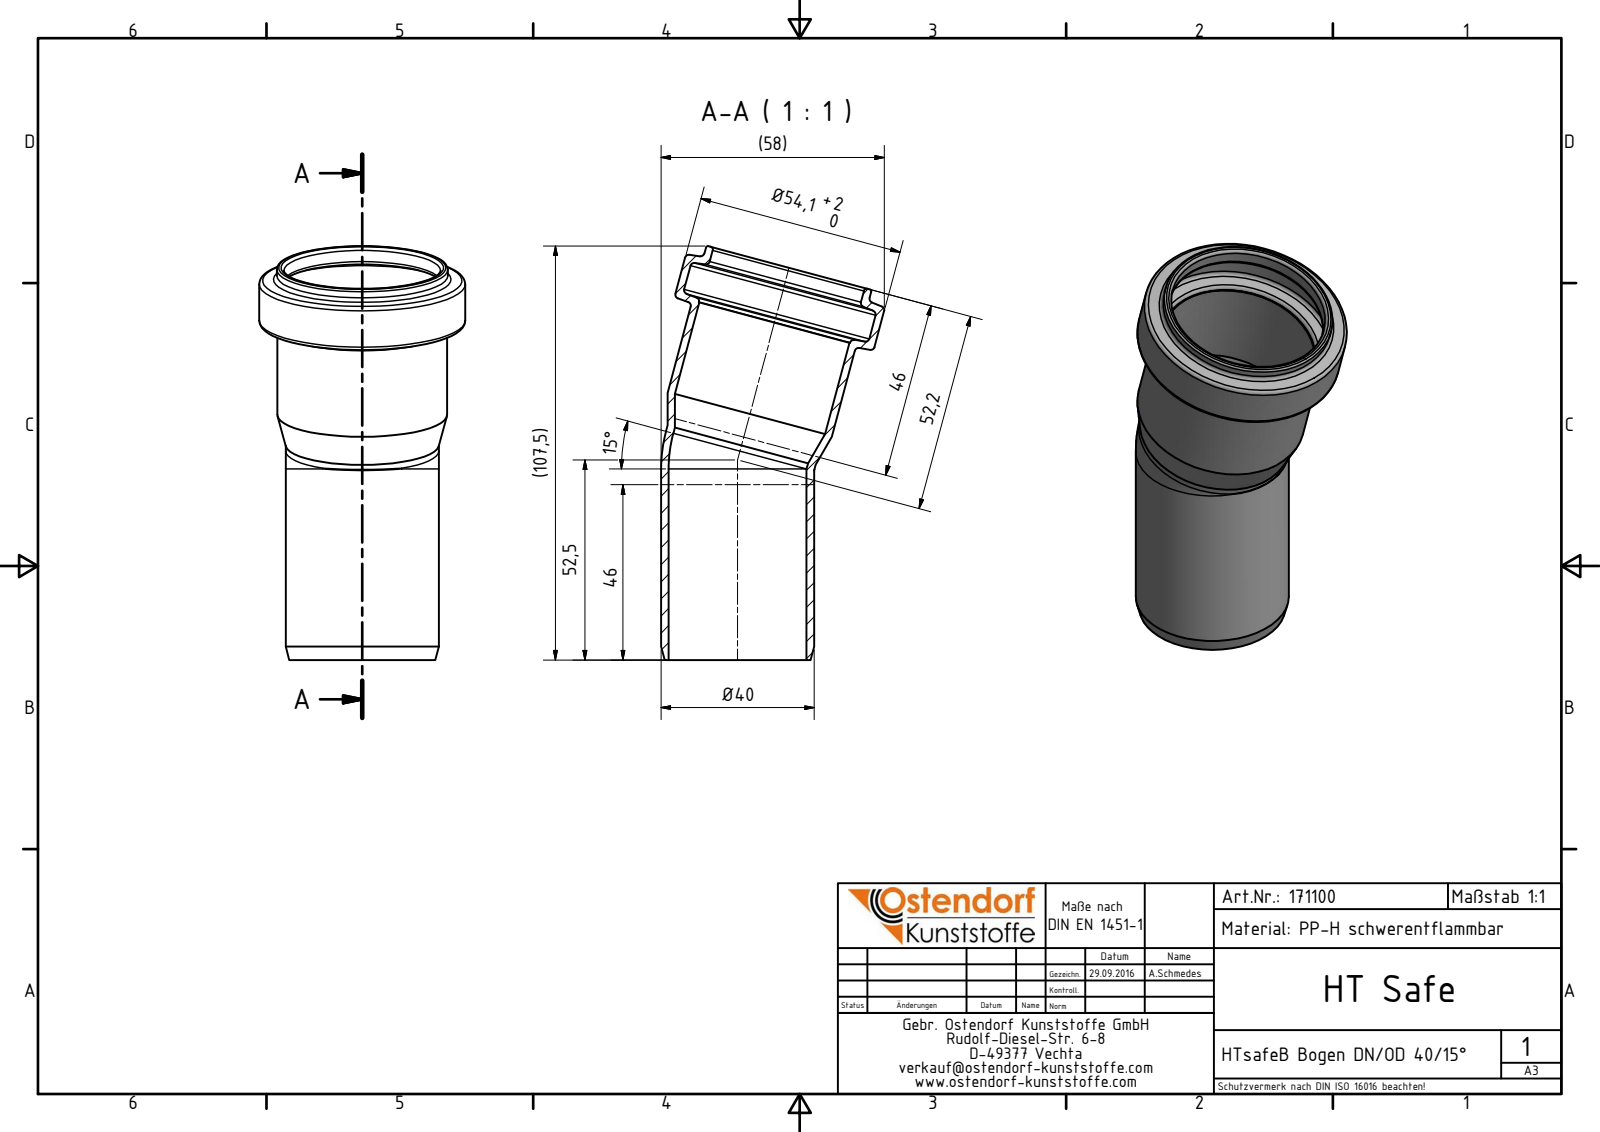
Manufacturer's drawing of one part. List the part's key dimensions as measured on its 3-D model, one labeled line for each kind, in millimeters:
Part name (STEP PRODUCT): 171100 HTsafeB DN_OD 40_15°
STEP written by: Autodesk Inventor 2016 (AUTOMOTIVE_DESIGN)
Units: millimetres
Bodies: 1 solid, 34 faces (3 planar, 11 cylindrical, 20 other)
Overall size (bounding box): 108.62 × 58.61 × 54.1
Volume: 28 454 mm³ · Surface area: 29 504 mm²
Round holes (diameter × count): ⌀36.2 ×2, ⌀41.1 ×2, ⌀40.8 ×1, ⌀50.3 ×1
Round bosses / shafts (diameter × count): ⌀40.2 ×2, ⌀54.1 ×1, ⌀44.9 ×1, ⌀44.6 ×1
Main face-to-face distances: 14.9
